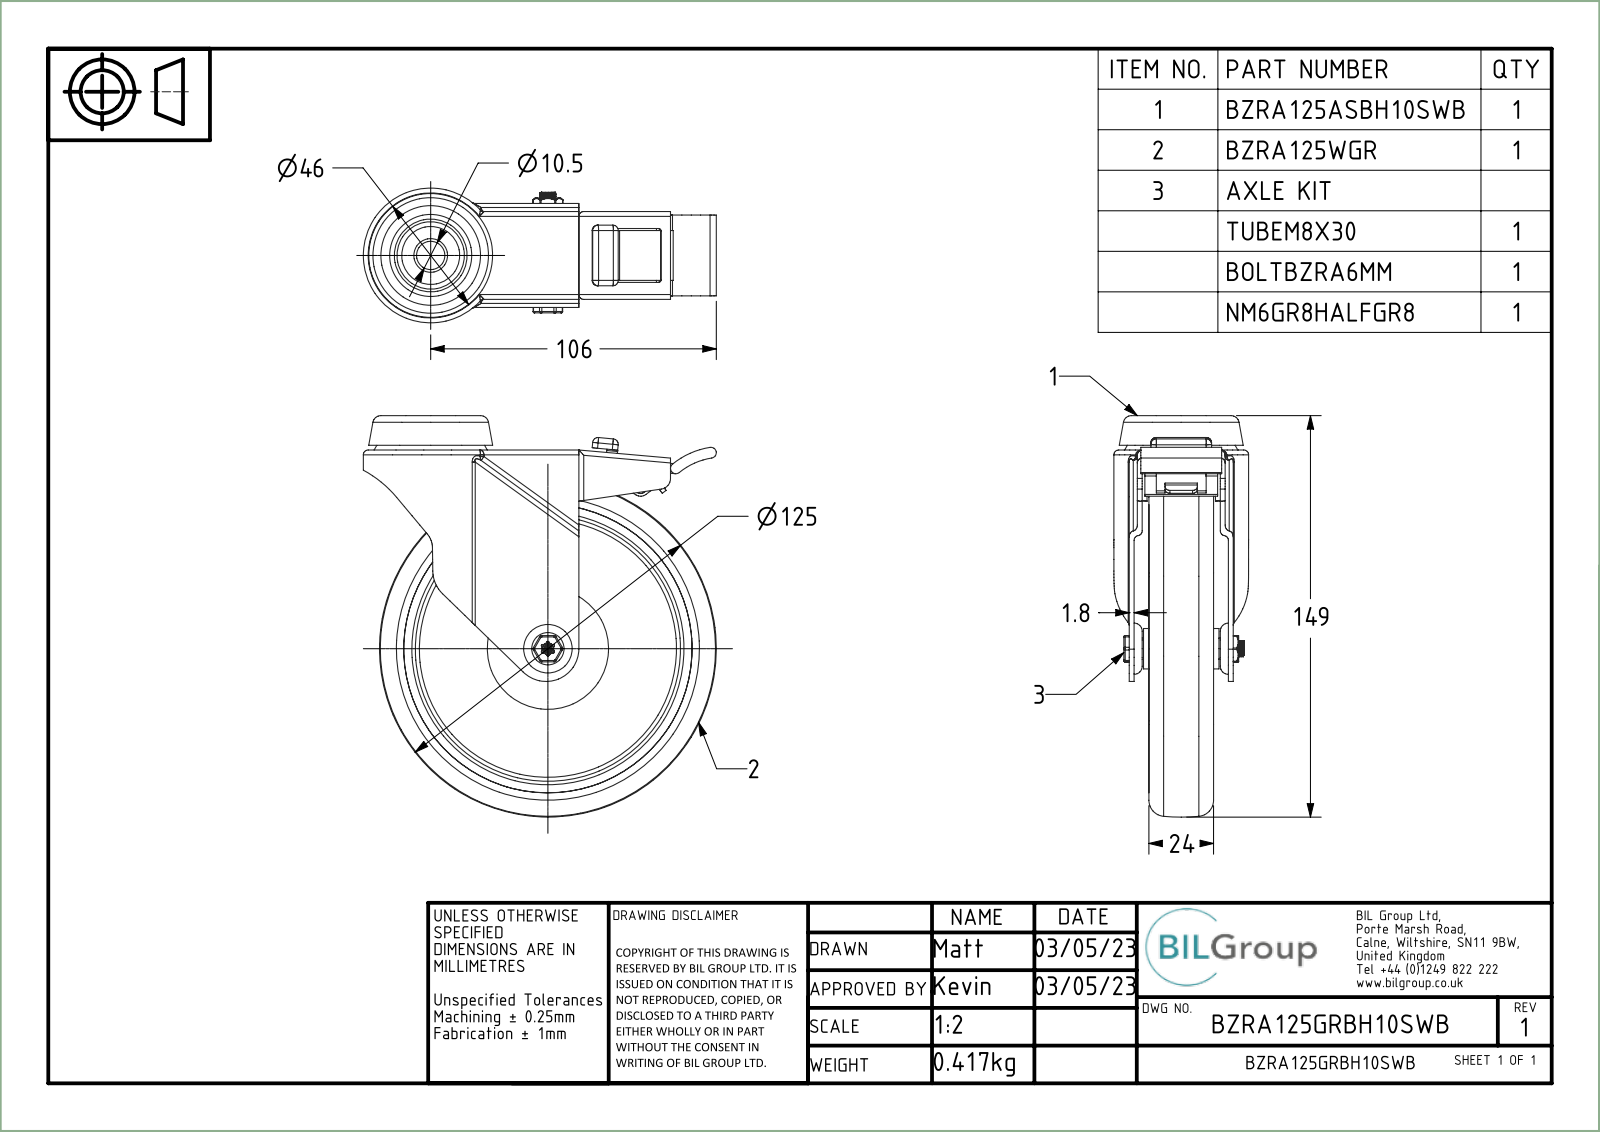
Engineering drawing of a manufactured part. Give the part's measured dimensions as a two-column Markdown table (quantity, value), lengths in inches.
| quantity | value |
| --- | --- |
| part name | BZRA125ASBH10SWB; ZINC PLATED PRESSED STEEL HEAD; ZINC PLATED PRESSED STEEL FORKS; ZINC PLATED PRESSED STEEL BRAKE (+8 more) |
| STEP written by | Spatial InterOp 3D (CONFIG_CONTROL_DESIGN) |
| units | inches |
| bodies | 10 solids, 641 faces (216 planar, 254 cylindrical, 171 other) |
| overall size | 5.866 × 5.157 × 1.969 |
| volume | 11.91 in³ |
| surface area | 158.6 in² |
| round holes (diameter × count) | 0.236 × 1, 0.248 × 1, 0.252 × 1, 0.323 × 1, 0.327 × 1, 0.413 × 1, 0.416 × 1, 1.102 × 1, 1.535 × 1, 4.213 × 1 |
| round bosses / shafts (diameter × count) | 0.709 × 1, 0.591 × 1, 0.581 × 1, 0.315 × 1, 0.313 × 1, 0.197 × 1 |
| partial cylindrical surfaces (radius × count) | 0.039 × 23, 0.071 × 23, 0.02 × 14, 0.035 × 11, 0.079 × 11, 0.016 × 6, 0.083 × 1, 0.09 × 1 |
| main face-to-face distances | 0.217, 0.071, 0.581, 1.331, 0.118, 0.652, 0.868, 0.287, 1.232, 0.364 |
